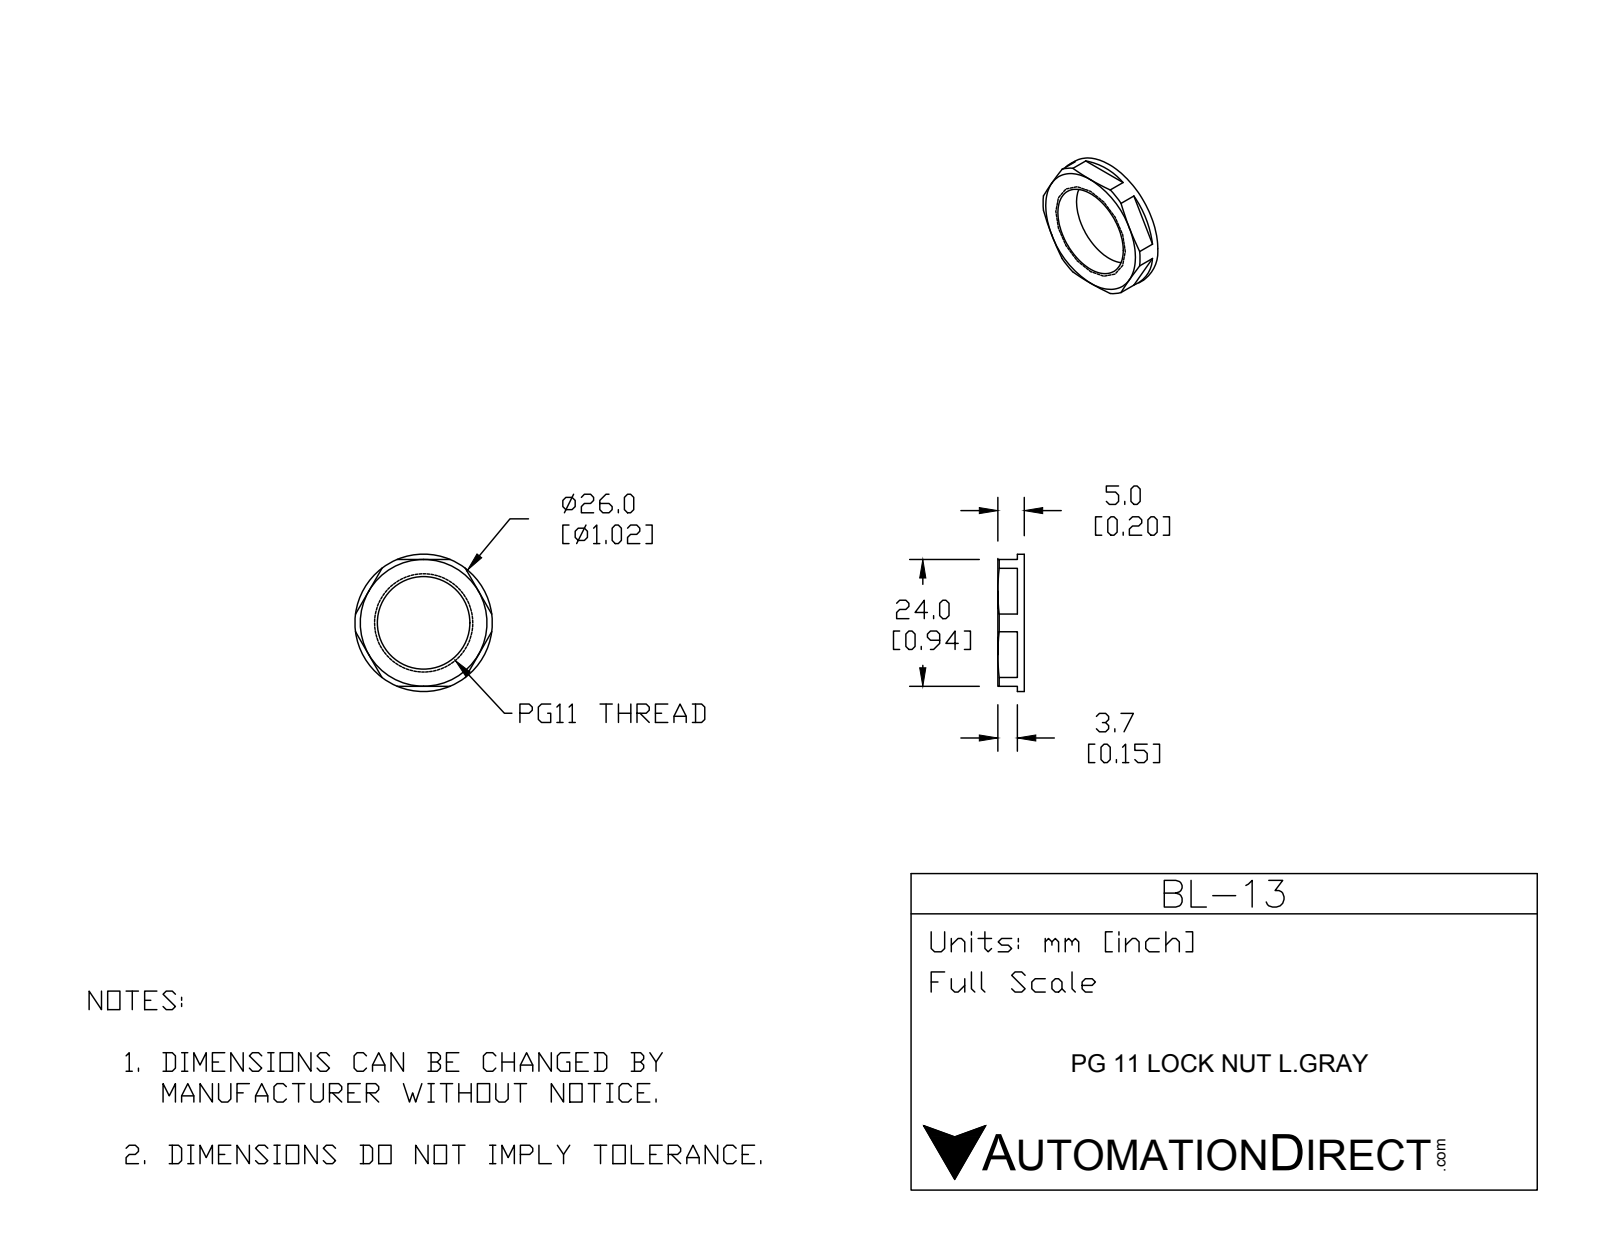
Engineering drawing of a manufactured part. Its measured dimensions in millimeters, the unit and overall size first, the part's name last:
Units: millimetres
Overall size (bounding box): 26 × 26 × 5
Round holes (diameter × count): ⌀1.5 ×3, ⌀17.5 ×1
Round bosses / shafts (diameter × count): ⌀26 ×1
Main face-to-face distances: 5, 24, 1.3, 3.7, 1, 4.7
Hole centre spacings: 11.55, 20, 20.01
Volume: 1 297 mm³ · Surface area: 1 253 mm²
Bodies: 1 solid, 33 faces (17 planar, 10 cylindrical, 6 other)
Part name (STEP PRODUCT): BL-13
STEP written by: SolidWorks 2015 (CONFIG_CONTROL_DESIGN)
